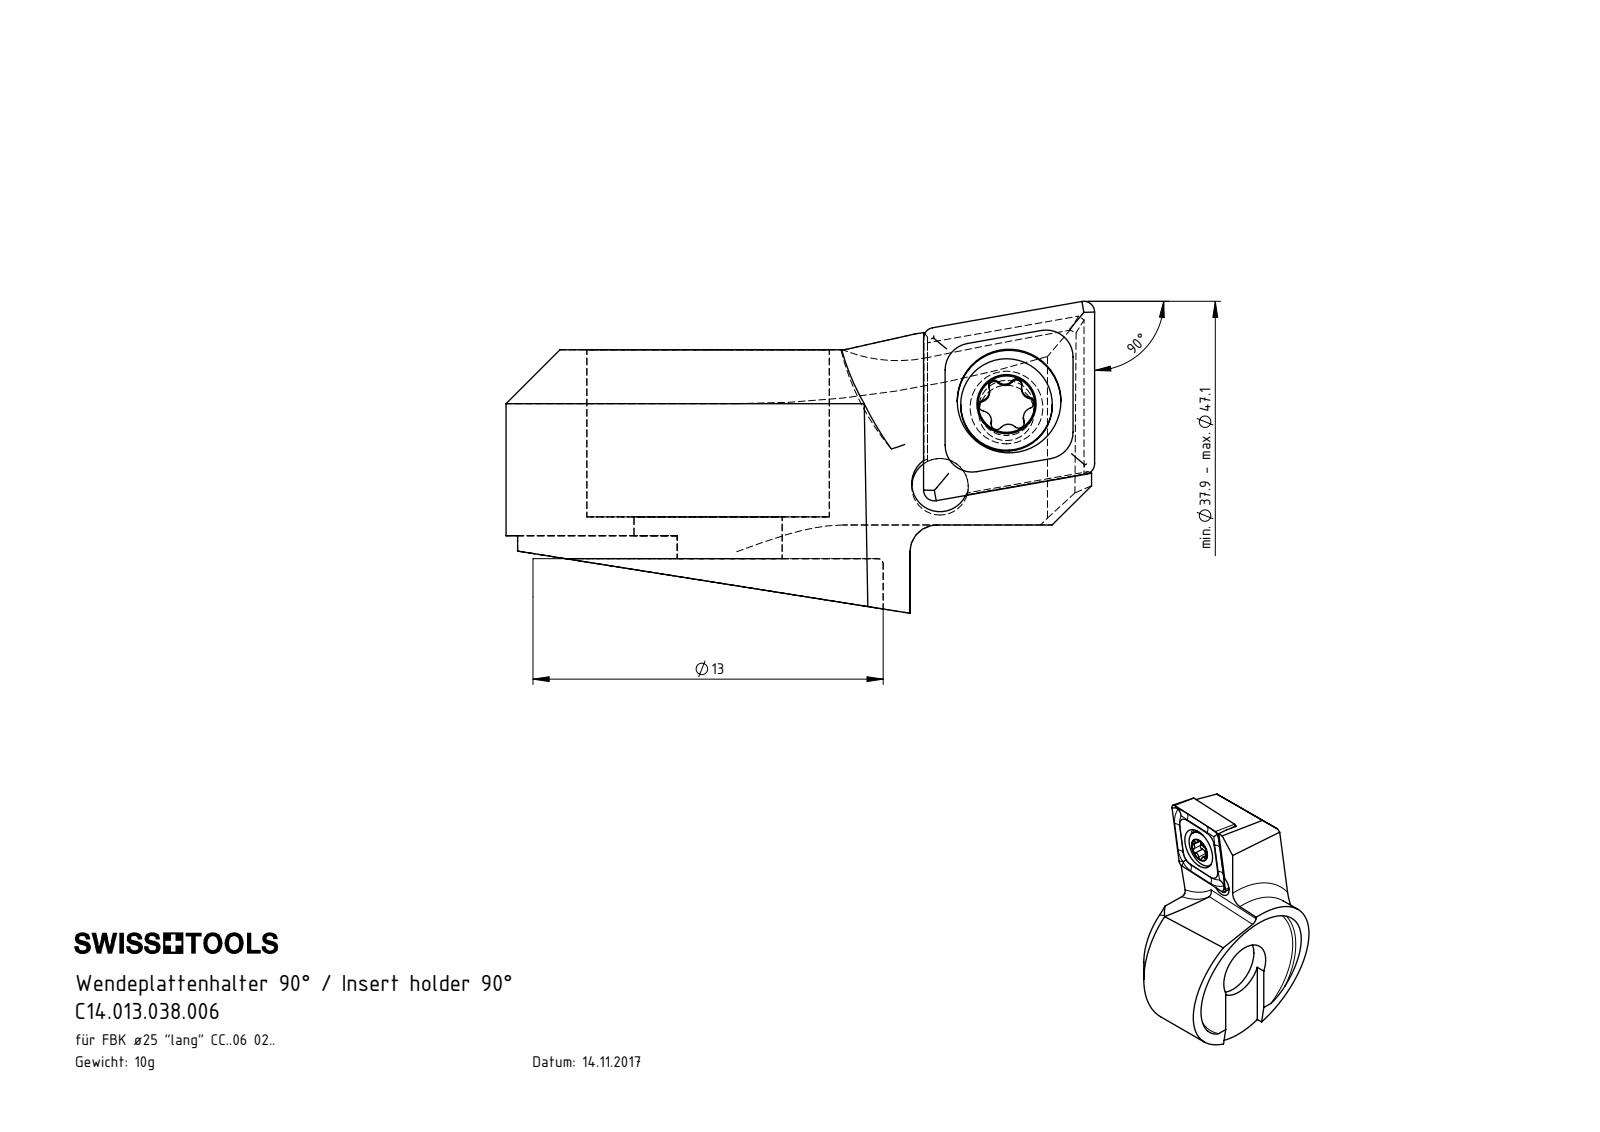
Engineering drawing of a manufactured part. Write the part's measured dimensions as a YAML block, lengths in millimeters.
part_name: "Kopie von F25-WCA.001.009_C^F25-WCA.001.009_fertigbearbeitet; CCMT060204; WCA-ER2.001.006_A; C14.013.038.006"
step_written_by: "SolidWorks 2017 (CONFIG_CONTROL_DESIGN)"
units: millimeters
bodies: {solids: 5, faces: 148, planar: 48, cylindrical: 45, other: 55}
overall_size: [21.85, 15, 11.58]
volume: 1269
surface_area: 1570
round_holes:
  - {diameter: 2.05, count: 1}
  - {diameter: 2.1, count: 1}
  - {diameter: 2.8, count: 1}
  - {diameter: 3.85, count: 1}
  - {diameter: 5.5, count: 1}
  - {diameter: 9, count: 1}
round_bosses_or_shafts:
  - {diameter: 15, count: 1}
  - {diameter: 3.4, count: 1}
  - {diameter: 2.5, count: 1}
partial_cylinders:
  - {radius: 0.21, count: 6}
  - {radius: 0.36, count: 5}
  - {radius: 0.5, count: 2}
  - {radius: 0.36, count: 1}
  - {radius: 1.05, count: 1}
  - {radius: 6.4, count: 1}
  - {radius: 6.5, count: 1}
  - {radius: 9, count: 1}
face_to_face_distances: [7.75, 7.65, 2.28, 6.2, 6.1, 1.55, 6.5, 6.4, 1.25, 6.9]
hole_center_spacings: [3.84, 3.99]
